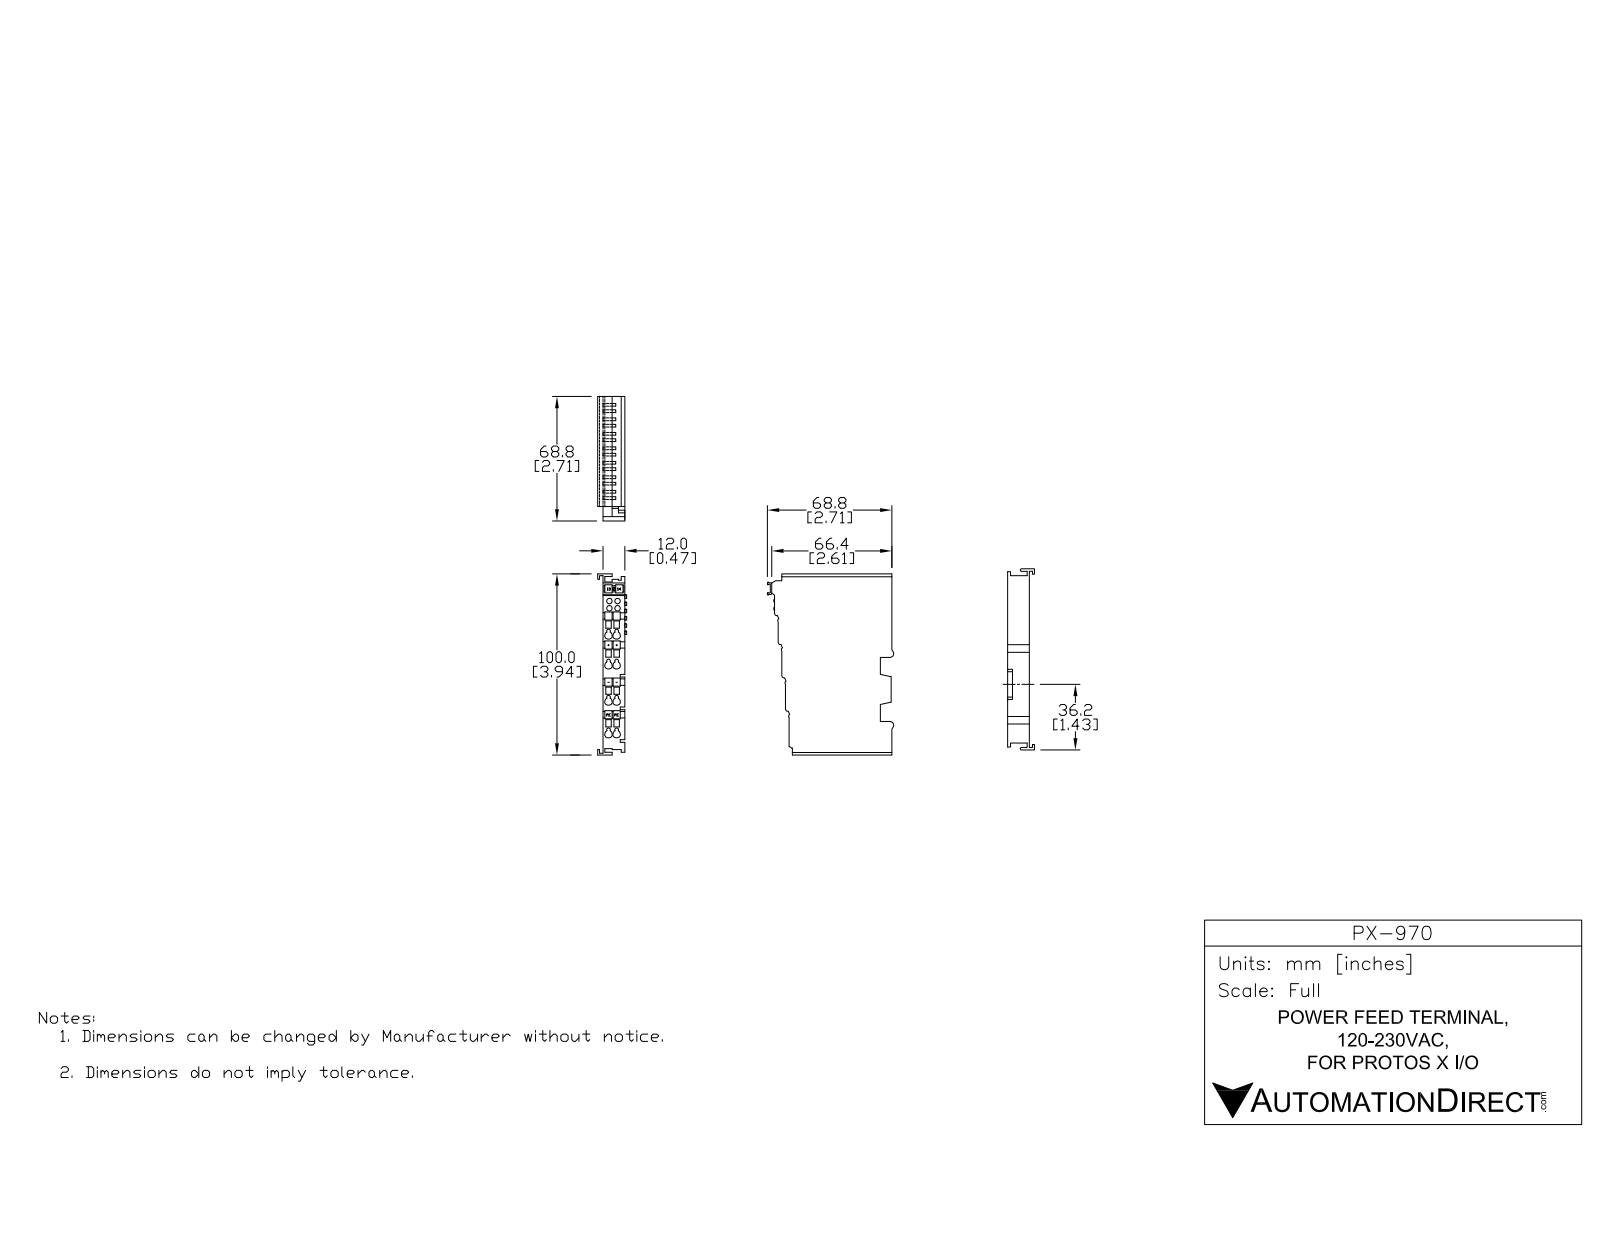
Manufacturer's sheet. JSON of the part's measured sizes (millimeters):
{"part_name": "PX-970", "step_written_by": "SolidWorks 2014 (AUTOMOTIVE_DESIGN)", "units": "millimeters", "bodies": {"solids": 28, "faces": 1367, "planar": 963, "cylindrical": 344, "other": 60}, "overall_size": [100.25, 71.26, 15.15], "volume_mm3": 58403, "surface_area_mm2": 33884, "round_holes": [[4, 8], [3.5, 4]], "partial_cylinders_radius": [[0.3, 46], [0.25, 35], [0.38, 12], [0.12, 10], [1, 9], [0.4, 8], [0.17, 4], [1.03, 4]], "face_to_face_distances": [12, 1, 2, 10, 1.85, 11, 8.7, 4, 3.15, 1.22], "hole_center_spacings": [4.5, 5, 18.4, 19.07, 6.36, 16, 16.76, 20.41]}
